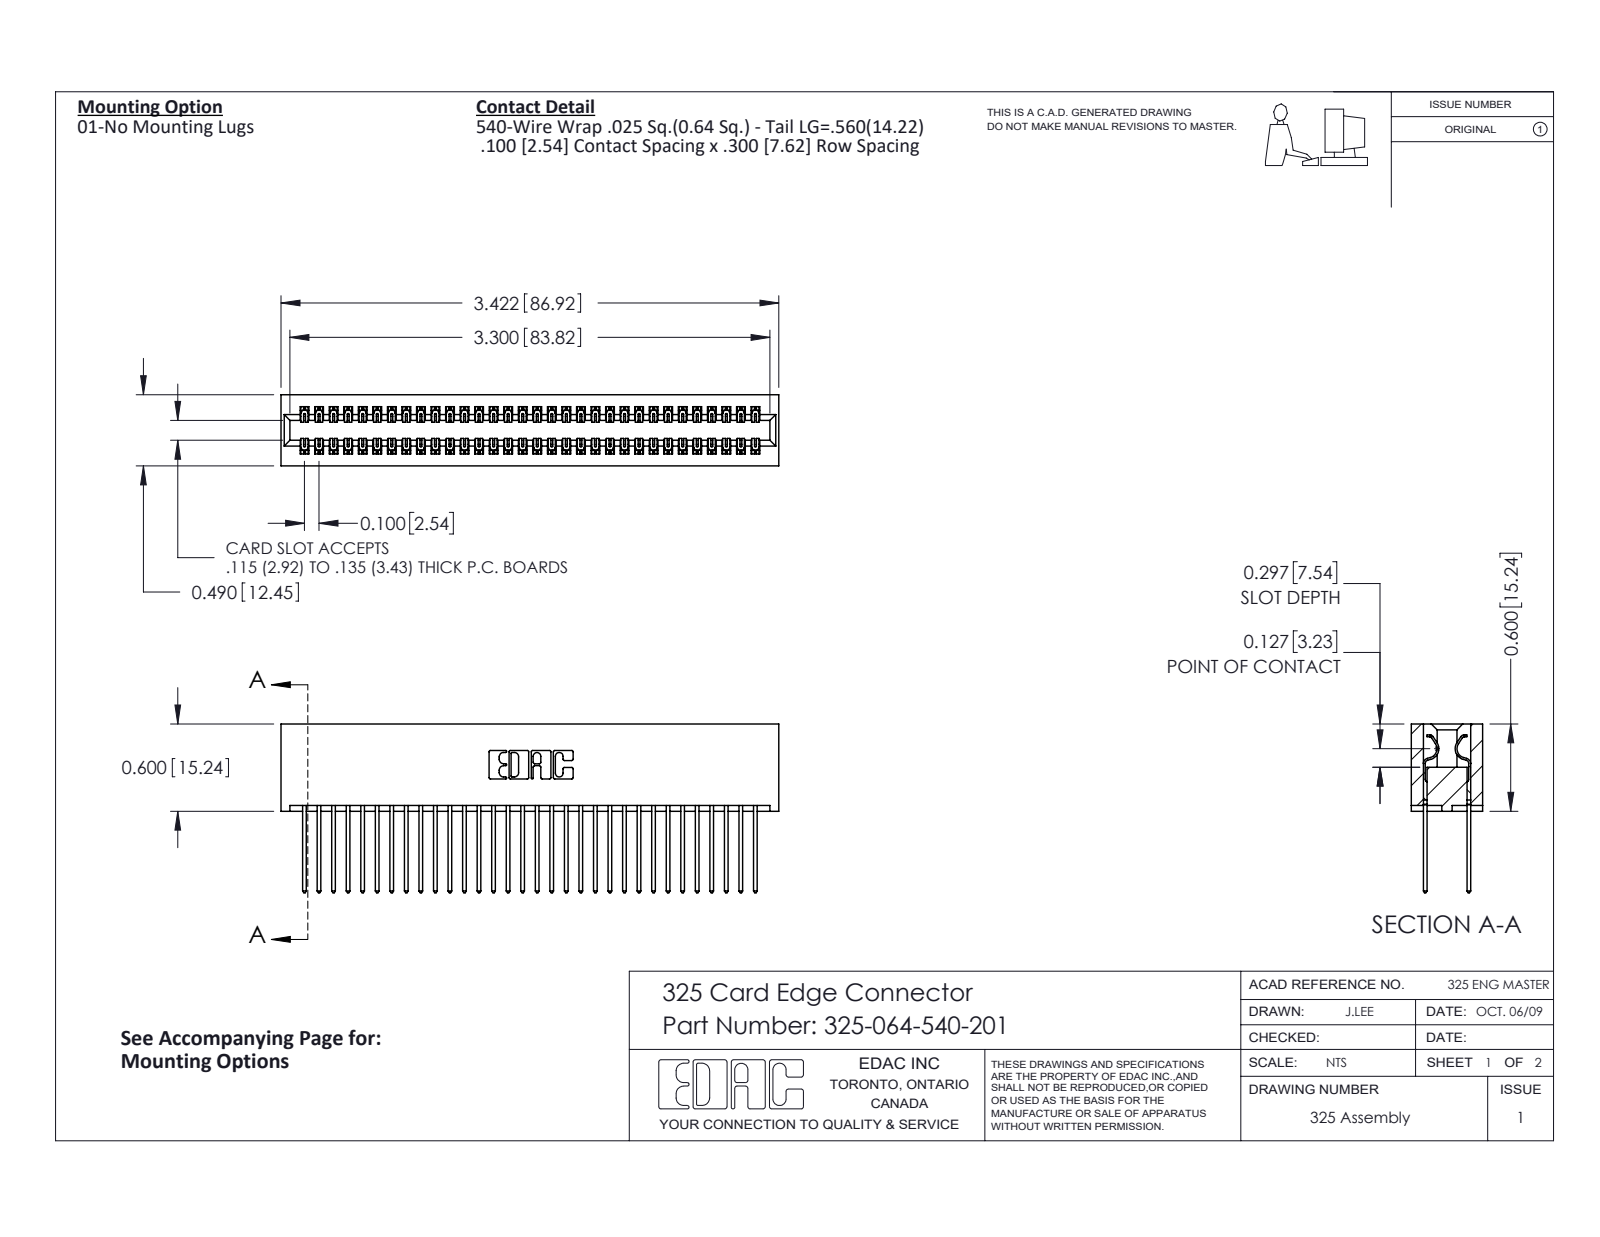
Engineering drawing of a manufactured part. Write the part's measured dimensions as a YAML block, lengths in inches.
part_name: "325-064-540-201; 325-292-001_325-293-140; 325 Part_Lugless"
step_written_by: "SolidWorks 2016 (CONFIG_CONTROL_DESIGN)"
units: inches
bodies: {solids: 65, faces: 3434, planar: 2370, cylindrical: 1064, other: 0}
overall_size: [3.422, 1.16, 0.49]
volume: 0.731
surface_area: 24.92
partial_cylinders:
  - {radius: 0.006, count: 96}
  - {radius: 0.01, count: 64}
  - {radius: 0.01, count: 22}
  - {radius: 0.007, count: 6}
  - {radius: 0.031, count: 6}
  - {radius: 0.026, count: 3}
  - {radius: 0.014, count: 2}
  - {radius: 0.022, count: 2}
face_to_face_distances: [0.083, 0.407, 0.3, 0.107, 0.383, 0.025, 0.325, 0.49, 0.275, 0.1]
